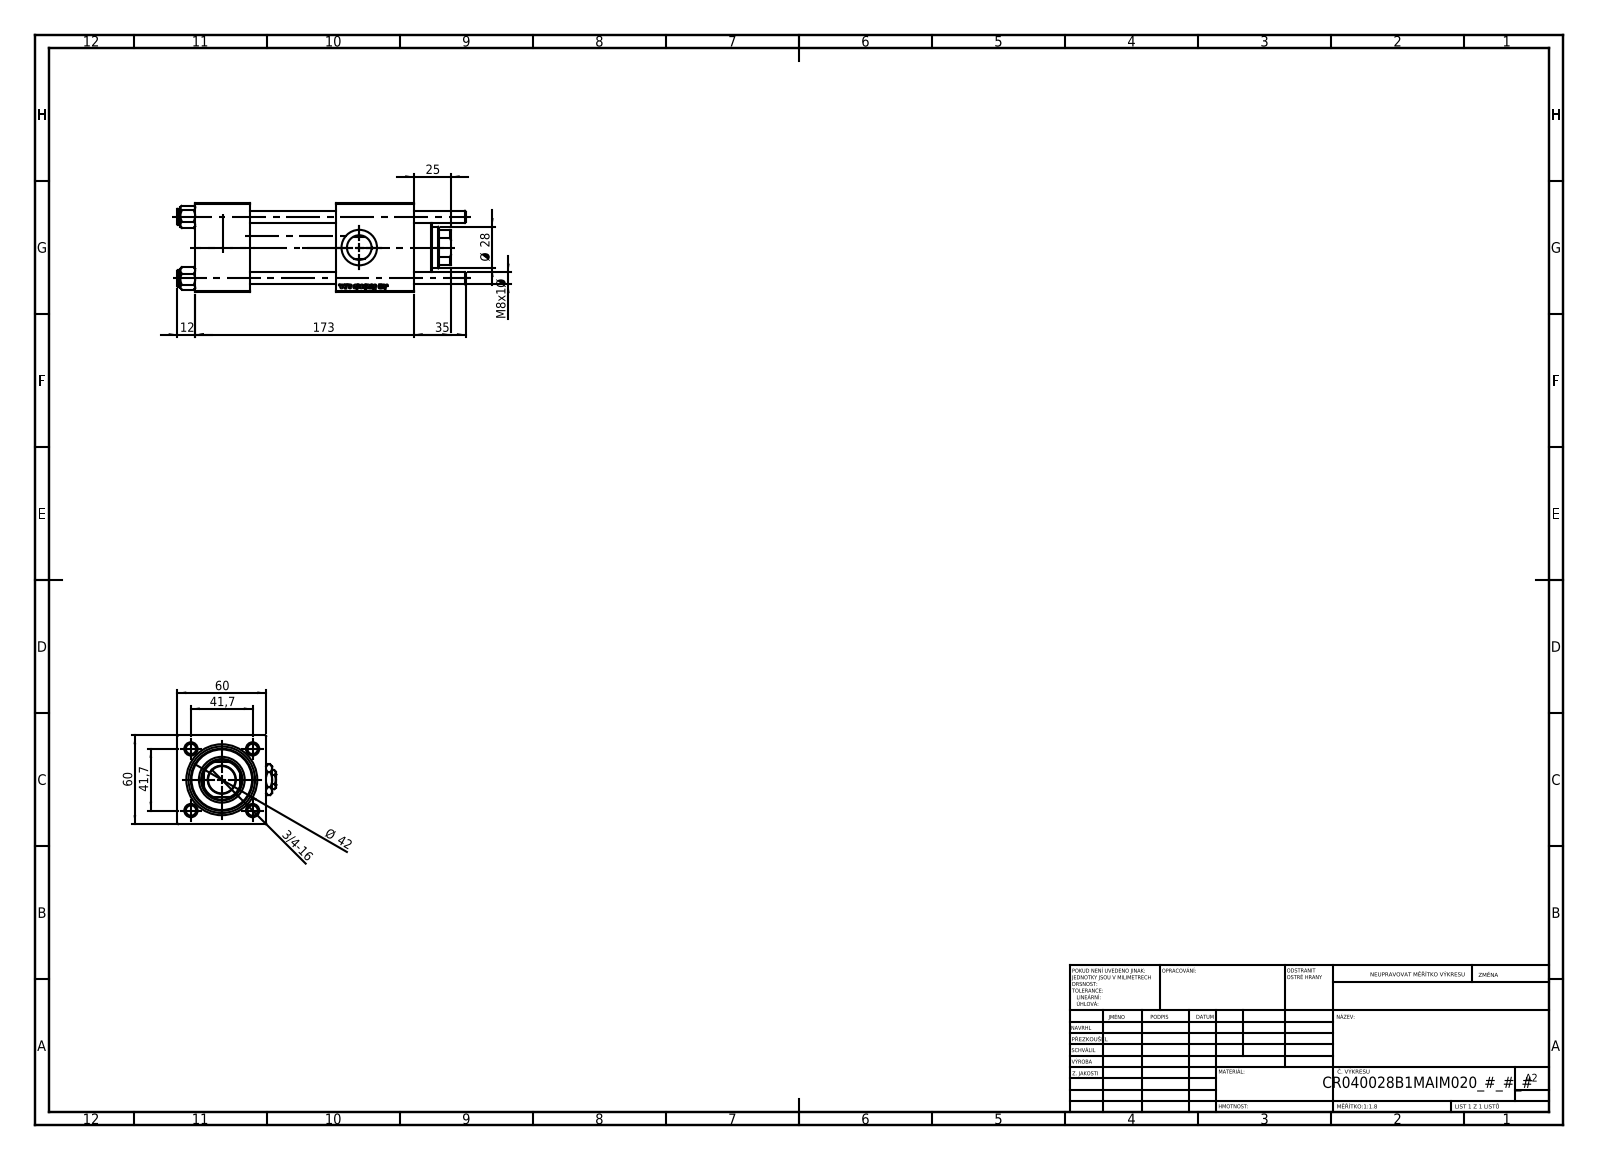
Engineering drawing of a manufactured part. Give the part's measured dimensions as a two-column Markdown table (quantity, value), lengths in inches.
| quantity | value |
| --- | --- |
| part name | V215CR_VCP_B; V215CR_B_TYCINKA; V215CR_B-1; V215_VC_A (+2 more) |
| STEP written by | SolidWorks 2019 (CONFIG_CONTROL_DESIGN) |
| units | inches |
| bodies | 12 solids, 1207 faces (456 planar, 83 cylindrical, 668 other) |
| overall size | 7.677 × 2.638 × 2.362 |
| volume | 26.45 in³ |
| surface area | 187.9 in² |
| round holes (diameter × count) | 0.315 × 4, 0.276 × 2, 0.656 × 2, 0.63 × 1, 0.728 × 1, 0.945 × 1, 1.102 × 1, 1.22 × 1, 1.575 × 1, 1.772 × 1 |
| round bosses / shafts (diameter × count) | 0.433 × 4, 1.811 × 1, 1.654 × 1 |
| partial cylindrical surfaces (radius × count) | 0.531 × 1 |
| main face-to-face distances | 2.362, 1.457, 2.283, 3.74, 2.087, 4.697, 3.24, 0.957, 5.827, 4.37 |
| hole center spacings | 1.161, 1.642, 2.322 |
